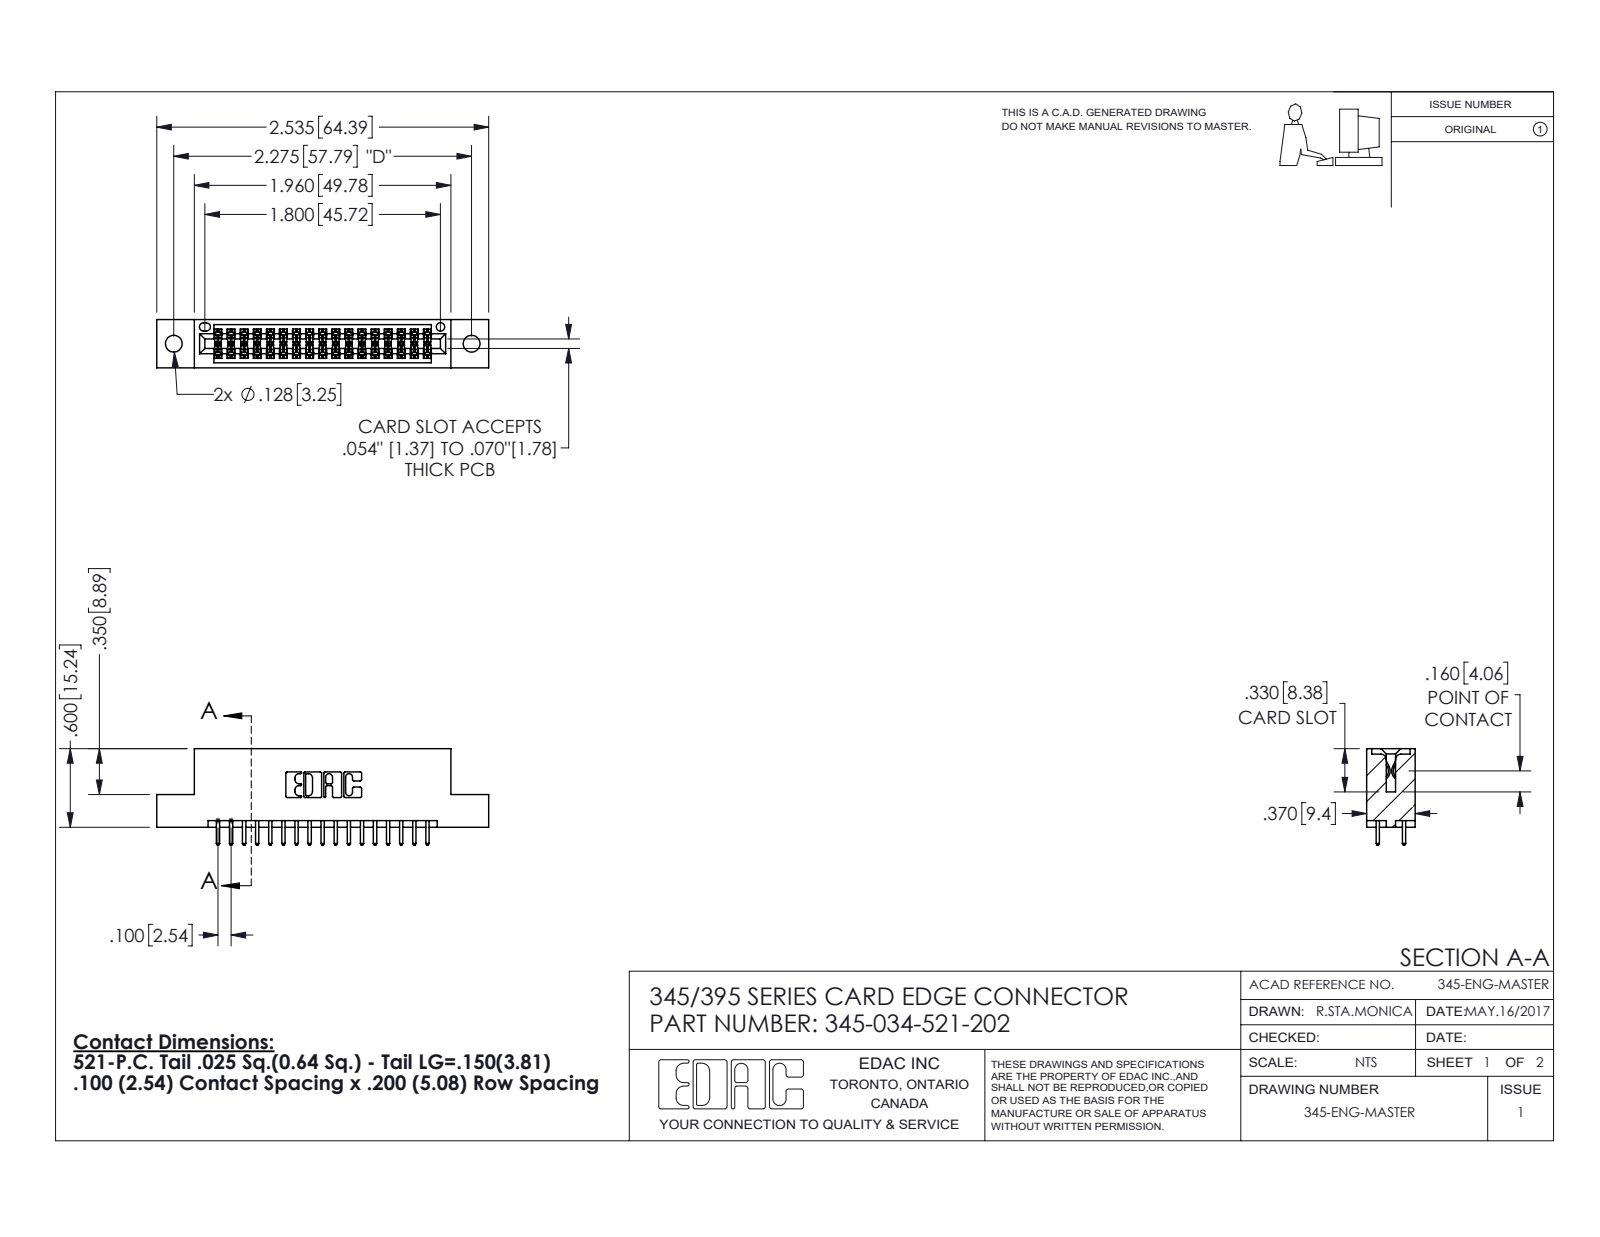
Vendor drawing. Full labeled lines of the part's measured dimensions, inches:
Part name (STEP PRODUCT): 345-034-521-202; 345-292-001_345-293-121; 345 Part_Flush Mounting Lugs - 0.128 Dia
STEP written by: SolidWorks 2016 (CONFIG_CONTROL_DESIGN)
Units: inches
Bodies: 35 solids, 1826 faces (1202 planar, 624 cylindrical, 0 other)
Overall size (bounding box): 2.535 × 0.737 × 0.37
Volume: 0.364 in³ · Surface area: 12.37 in²
Round holes (diameter × count): ⌀0.128 ×2, ⌀0.064 ×1
Partial cylindrical surfaces — rounded edges, fillets, slot ends (radius × count): R0.006 ×51, R0.01 ×34, R0.01 ×22, R0.007 ×6, R0.031 ×6, R0.026 ×3, R0.014 ×2, R0.019 ×2
Main face-to-face distances: 0.298, 0.072, 0.2, 0.37, 0.098, 0.272, 0.025, 0.225, 0.1, 0.175
Hole centre spacings: 0.27, 2.041, 2.275
